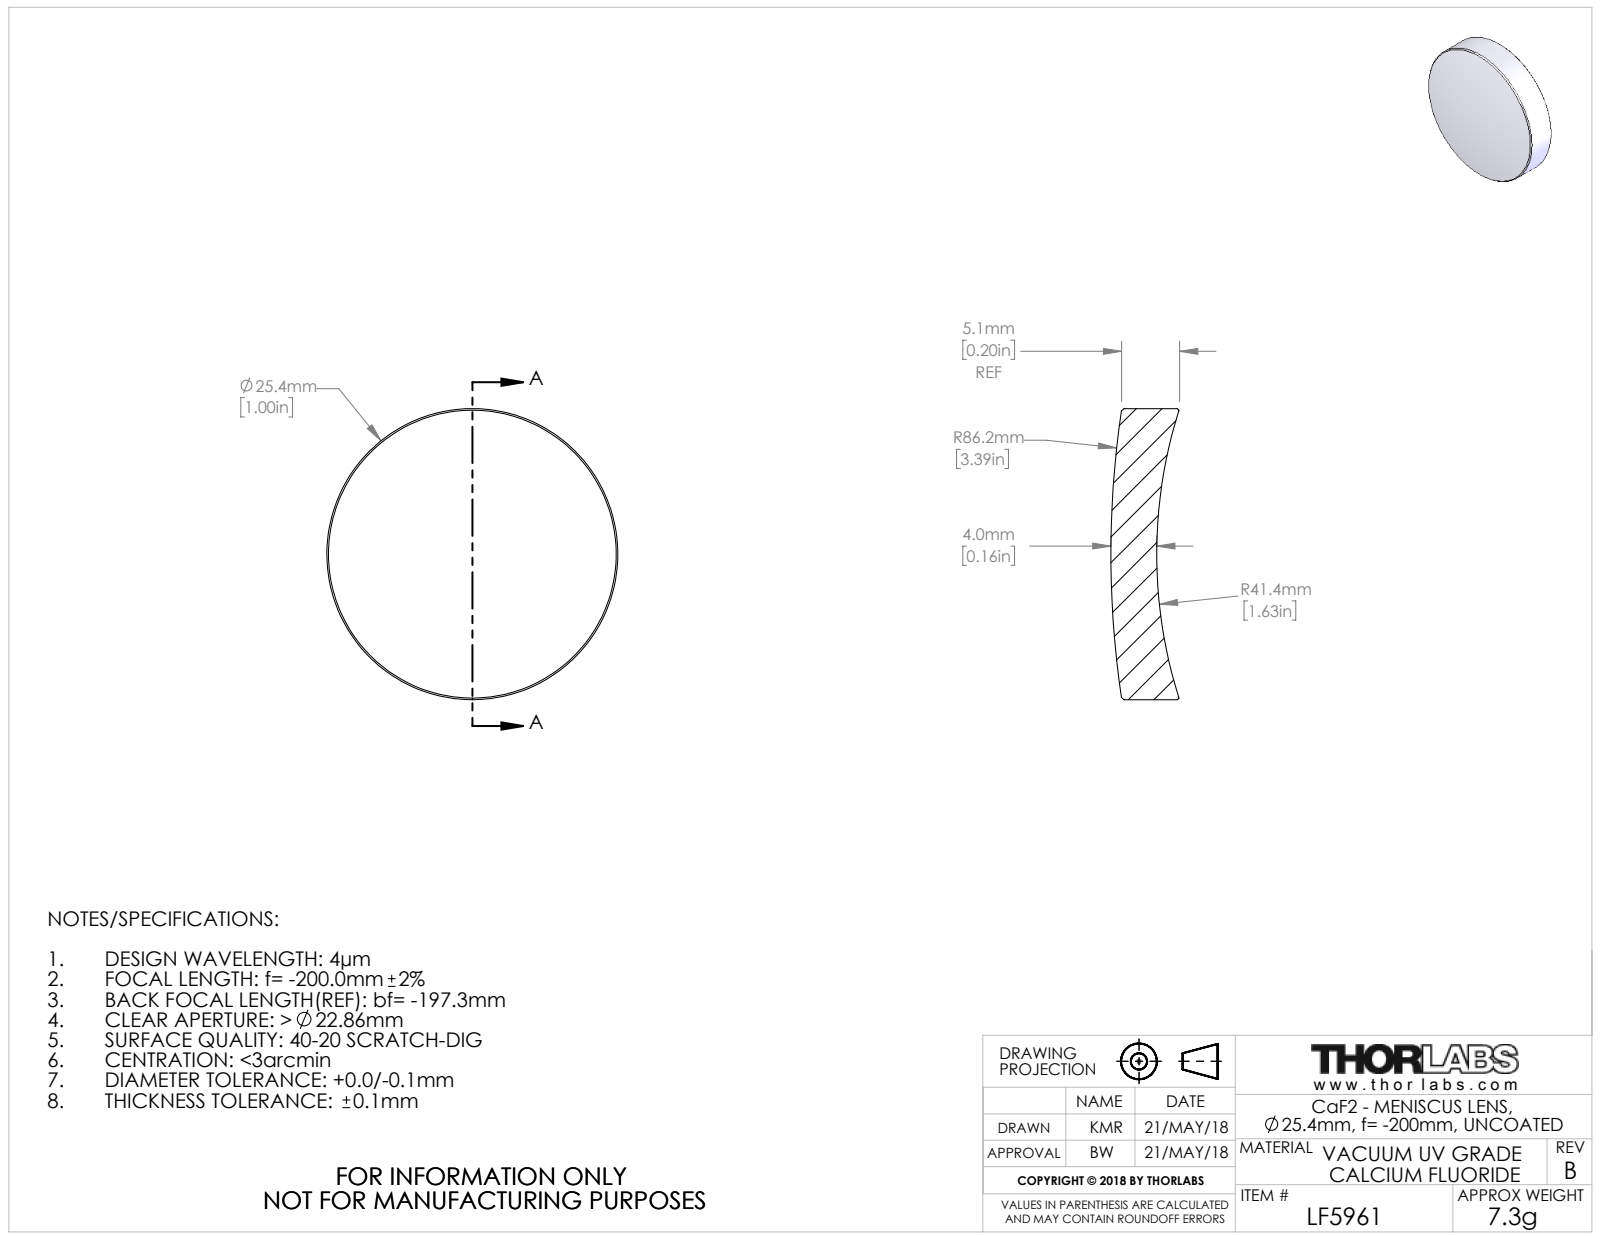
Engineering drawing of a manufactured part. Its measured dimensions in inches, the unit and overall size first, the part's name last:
Units: inches
Overall size (bounding box): 1 × 1 × 0.234
Round bosses / shafts (diameter × count): ⌀1 ×1
Volume: 0.14 in³ · Surface area: 2.191 in²
Bodies: 1 solid, 10 faces (0 planar, 2 cylindrical, 8 other)
Part name (STEP PRODUCT): 22003-E0W
STEP written by: SolidWorks 2016 (CONFIG_CONTROL_DESIGN)
